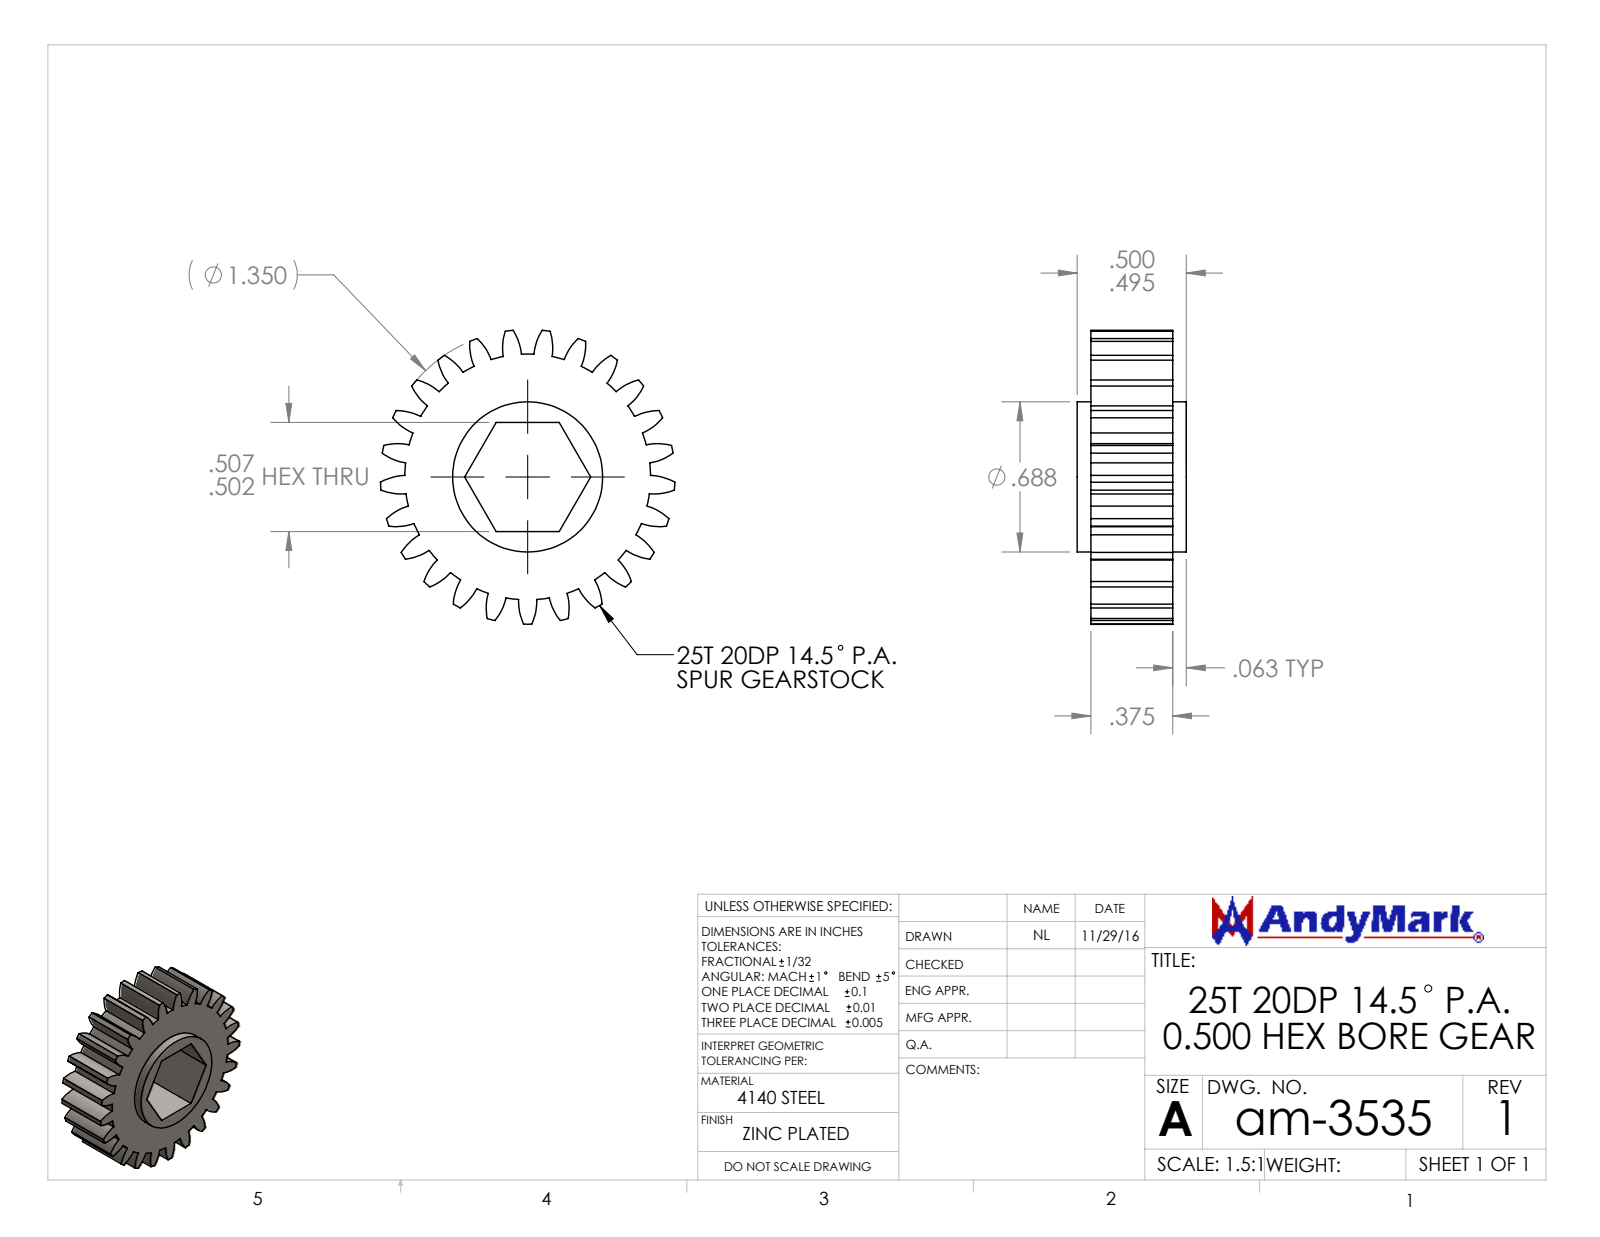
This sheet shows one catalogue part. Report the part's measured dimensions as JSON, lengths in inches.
{"part_name": "am-3535 25T 20DP 500hex 375 FW", "step_written_by": "SolidWorks 2022 (CONFIG_CONTROL_DESIGN)", "units": "inches", "bodies": {"solids": 1, "faces": 172, "planar": 10, "cylindrical": 108, "other": 54}, "overall_size": [1.349, 1.347, 0.5], "volume_in3": 0.389, "surface_area_in2": 6.025, "round_bosses_or_shafts": [[0.75, 1]], "partial_cylinders_radius": [[0.25, 50], [0.563, 1], [0.675, 1]], "face_to_face_distances": [0.375, 0.5, 0.437, 0.062, 0.063, 0.438]}
